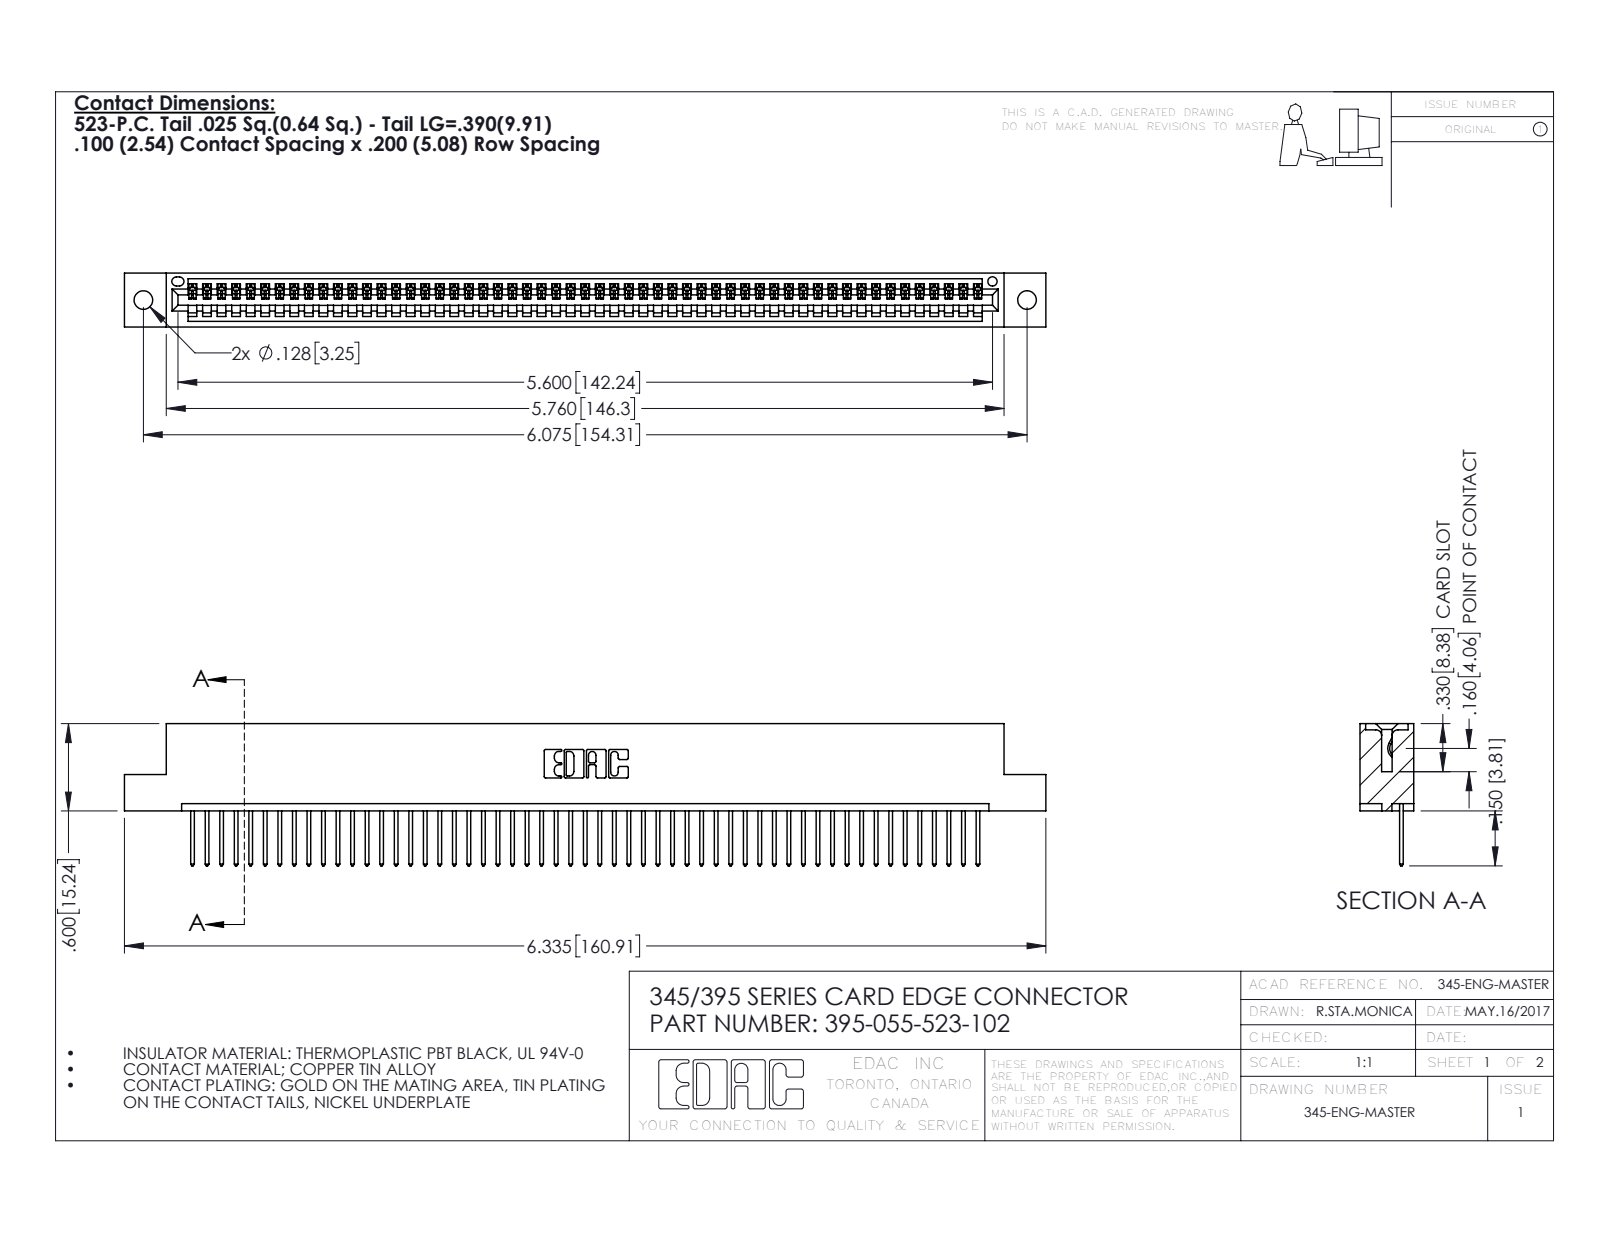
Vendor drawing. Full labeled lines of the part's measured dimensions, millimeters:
Part name (STEP PRODUCT): 345 Part_Flush Mounting Lugs - 0.128 Dia; 345-292-001_345-293-123; 395-055-523-102
STEP written by: SolidWorks 2016 (CONFIG_CONTROL_DESIGN)
Units: millimetres
Bodies: 56 solids, 3316 faces (2280 planar, 1036 cylindrical, 0 other)
Overall size (bounding box): 160.9 × 24.8 × 9.4
Volume: 15 300 mm³ · Surface area: 20 340 mm²
Round holes (diameter × count): ⌀3.3 ×2, ⌀1.6 ×1
Partial cylindrical surfaces — rounded edges, fillets, slot ends (radius × count): R0.2 ×110, R0.3 ×110, R0.3 ×22, R0.2 ×6, R0.8 ×6, R0.7 ×3, R0.8 ×2, R1 ×2
Main face-to-face distances: 7.6, 1.8, 9.4, 5.1, 2.5, 6.9, 0.6, 5.7, 3.8, 1.8
Hole centre spacings: 6.9, 148.3, 154.3
